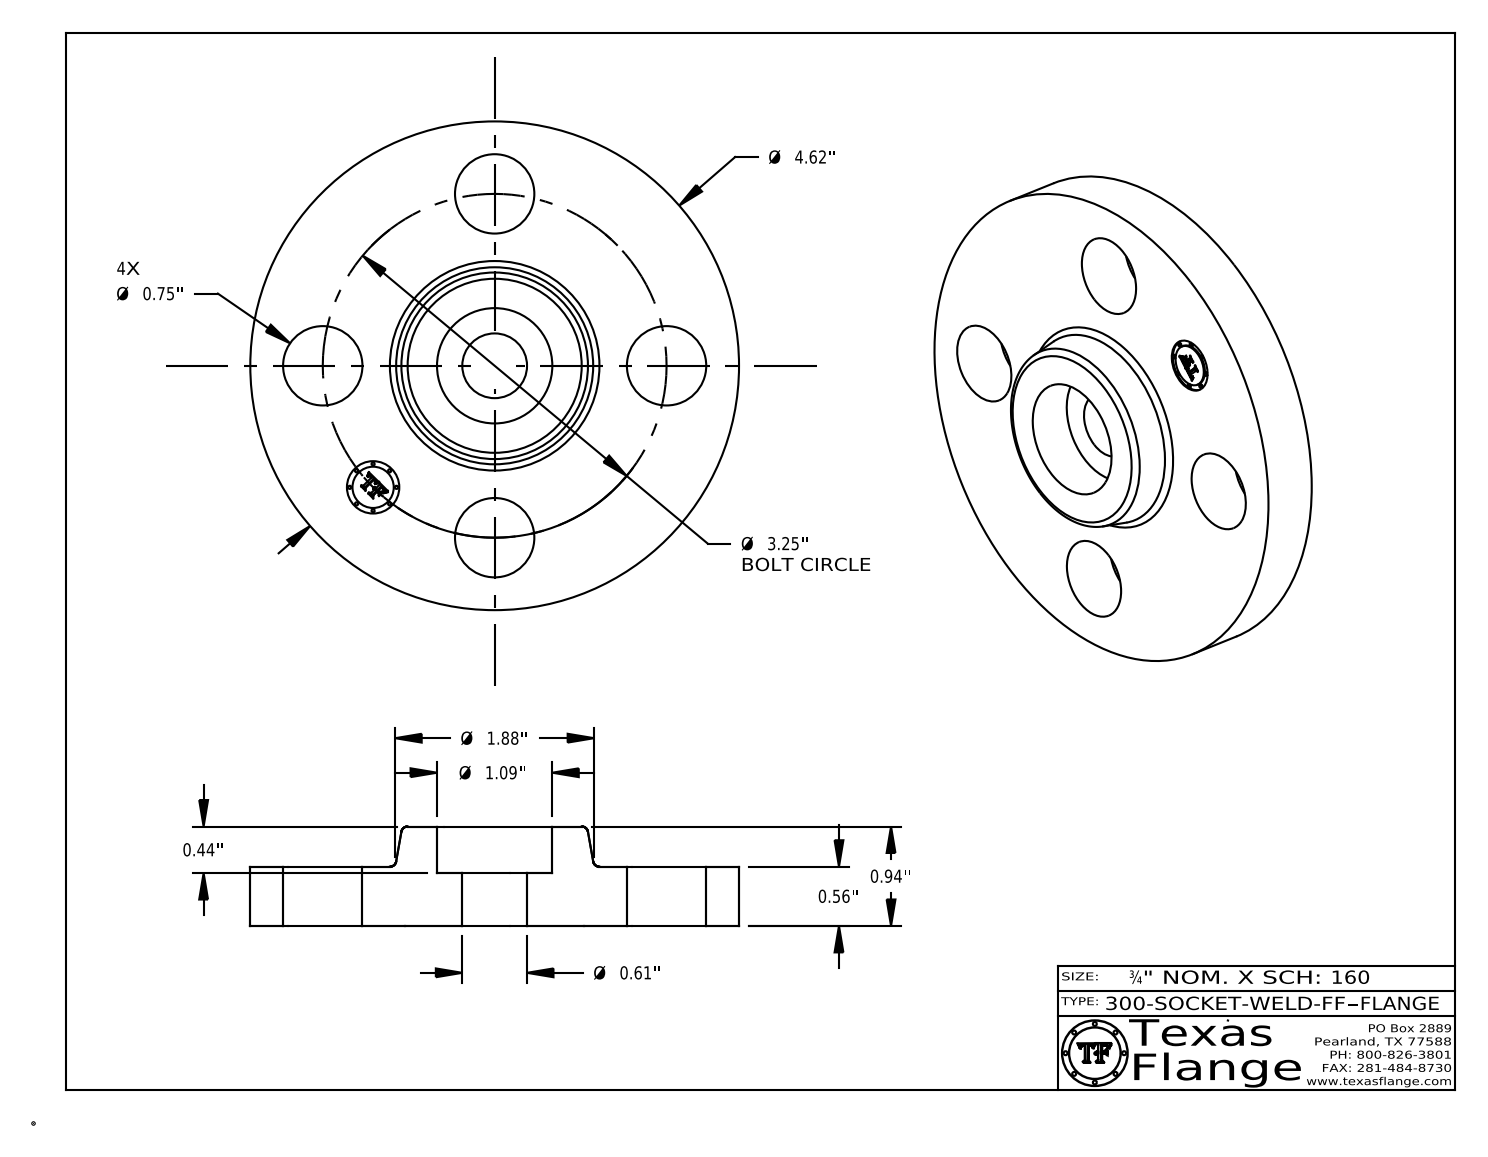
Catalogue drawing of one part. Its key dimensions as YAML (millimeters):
part_name: "300-SOCKET-WELD-FF"
step_written_by: "CATIA V5 STEP AP214 (AUTOMOTIVE_DESIGN)"
units: millimeters
bodies: {solids: 1, faces: 410, planar: 370, cylindrical: 34, other: 6}
overall_size: [117.3, 117.3, 23.9]
volume: 144600
surface_area: 30320
round_holes:
  - {diameter: 19.1, count: 4}
  - {diameter: 12.6, count: 1}
  - {diameter: 15.5, count: 1}
  - {diameter: 27.7, count: 1}
round_bosses_or_shafts:
  - {diameter: 0.8, count: 8}
  - {diameter: 117.3, count: 1}
  - {diameter: 9.9, count: 1}
face_to_face_distances: [14.2, 23.9, 9.7, 12.7, 1.5, 11.2, 13.8, 1.1, 0.4, 10]
hole_center_spacings: [41.3, 58.4, 31.6, 76.3, 82.6]
